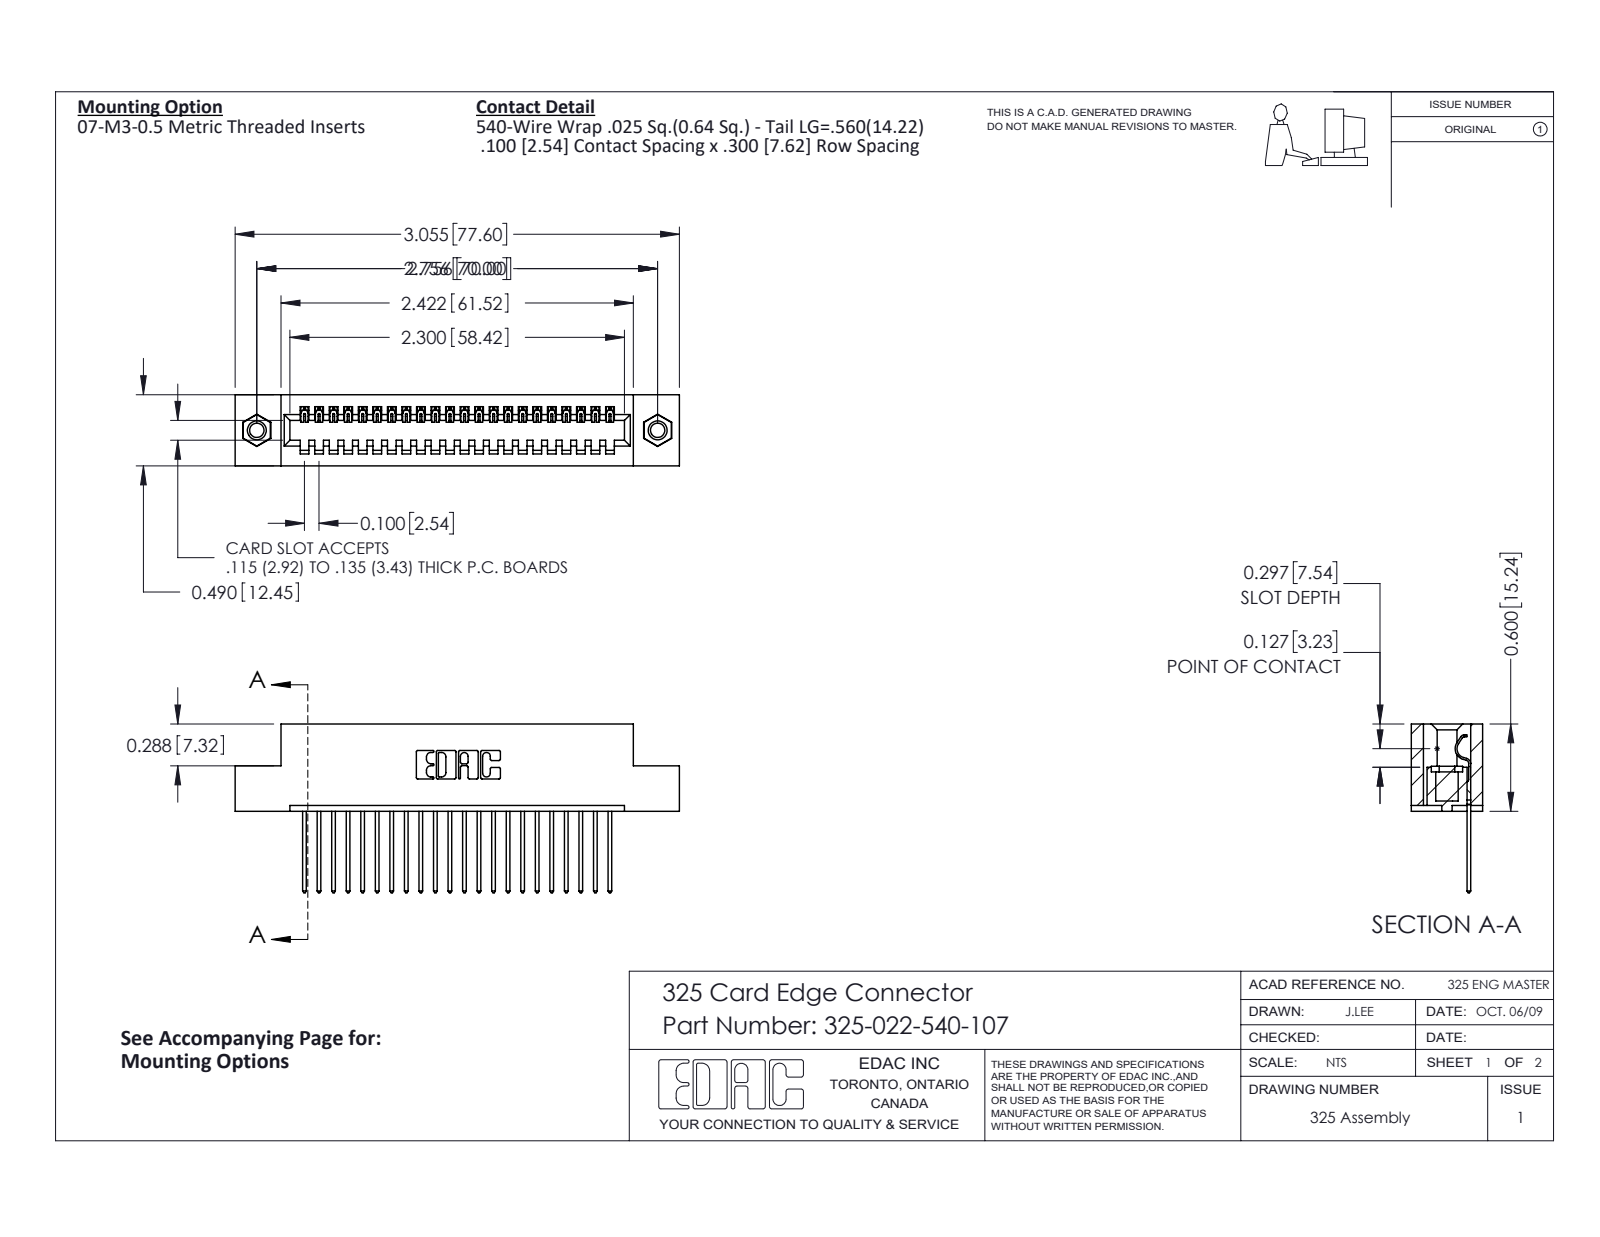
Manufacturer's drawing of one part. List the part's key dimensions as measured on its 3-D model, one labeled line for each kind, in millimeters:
Part name (STEP PRODUCT): 345-250-001_345-250-005-103; 325 Part_TI; 325-292-001_325-293-140; 325-022-540-107
STEP written by: SolidWorks 2016 (CONFIG_CONTROL_DESIGN)
Units: millimetres
Bodies: 25 solids, 1450 faces (1026 planar, 408 cylindrical, 16 other)
Overall size (bounding box): 77.6 × 29.5 × 12.4
Volume: 9 720 mm³ · Surface area: 10 520 mm²
Round holes (diameter × count): ⌀2.5 ×2, ⌀3.2 ×2, ⌀4.1 ×2
Round bosses / shafts (diameter × count): ⌀3.9 ×2
Partial cylindrical surfaces — rounded edges, fillets, slot ends (radius × count): R0.2 ×44, R0.3 ×44, R0.3 ×22, R0.2 ×6, R0.8 ×6, R0.7 ×3, R0.4 ×1, R0.6 ×1
Main face-to-face distances: 2.1, 10.3, 7.6, 12.4, 2.7, 9.7, 0.6, 1, 8.3, 2.5
Hole centre spacings: 70
